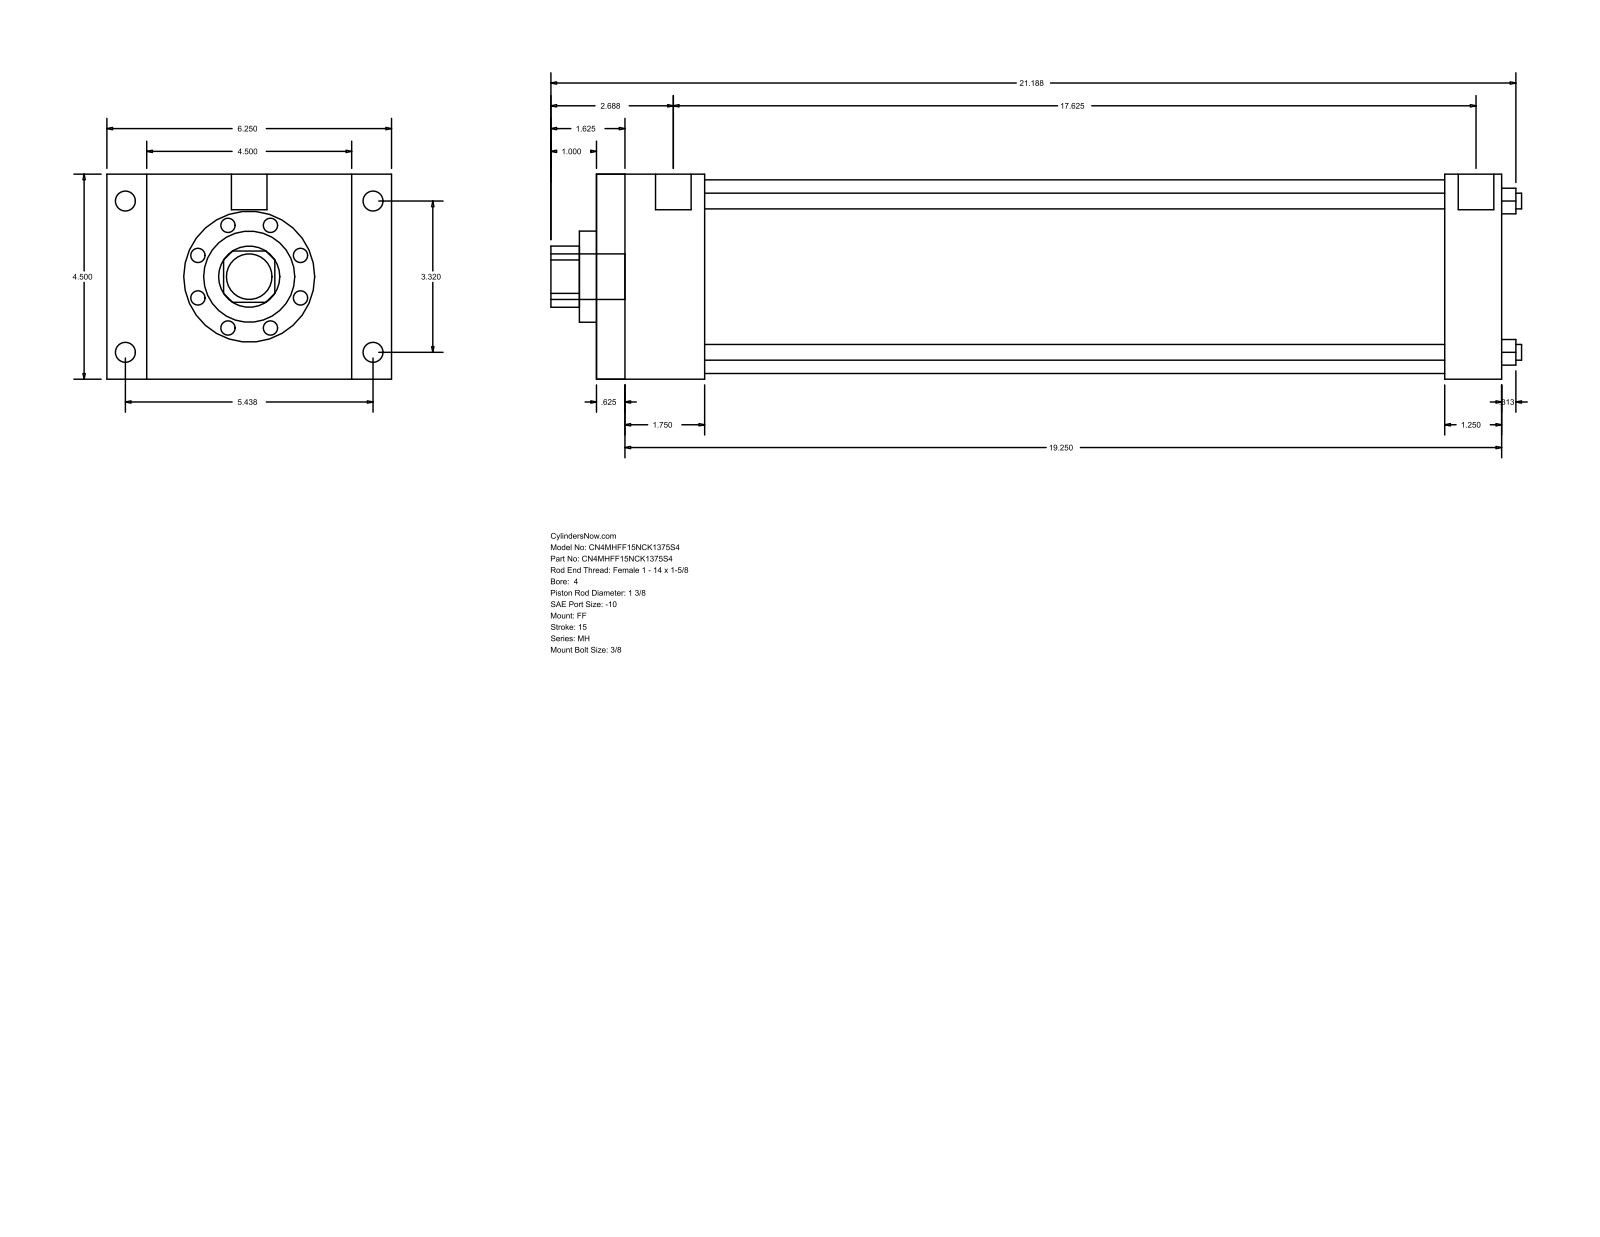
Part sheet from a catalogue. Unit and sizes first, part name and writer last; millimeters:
Units: millimetres
Overall size (bounding box): 541.34 × 158.75 × 114.3
Round holes (diameter × count): ⌀8.76 ×4, ⌀34.92 ×1, ⌀50.8 ×1, ⌀107.95 ×1
Round bosses / shafts (diameter × count): ⌀11.13 ×4, ⌀8.73 ×4, ⌀19.84 ×2, ⌀25.4 ×1
Partial cylindrical surfaces — rounded edges, fillets, slot ends (radius × count): R17.06 ×1
Main face-to-face distances: 114.3, 504.83, 15.87, 488.96, 60.32, 44.45, 444.51, 473.08, 457.21, 412.76
Hole centre spacings: 59.62, 84.32, 119.25
Bodies: 0 solids, 92 faces (64 planar, 28 cylindrical, 0 other)
Part name (STEP PRODUCT): MH_FF__0400_1.375
STEP written by: GSSL Pune (CONFIG_CONTROL_DESIGN)
